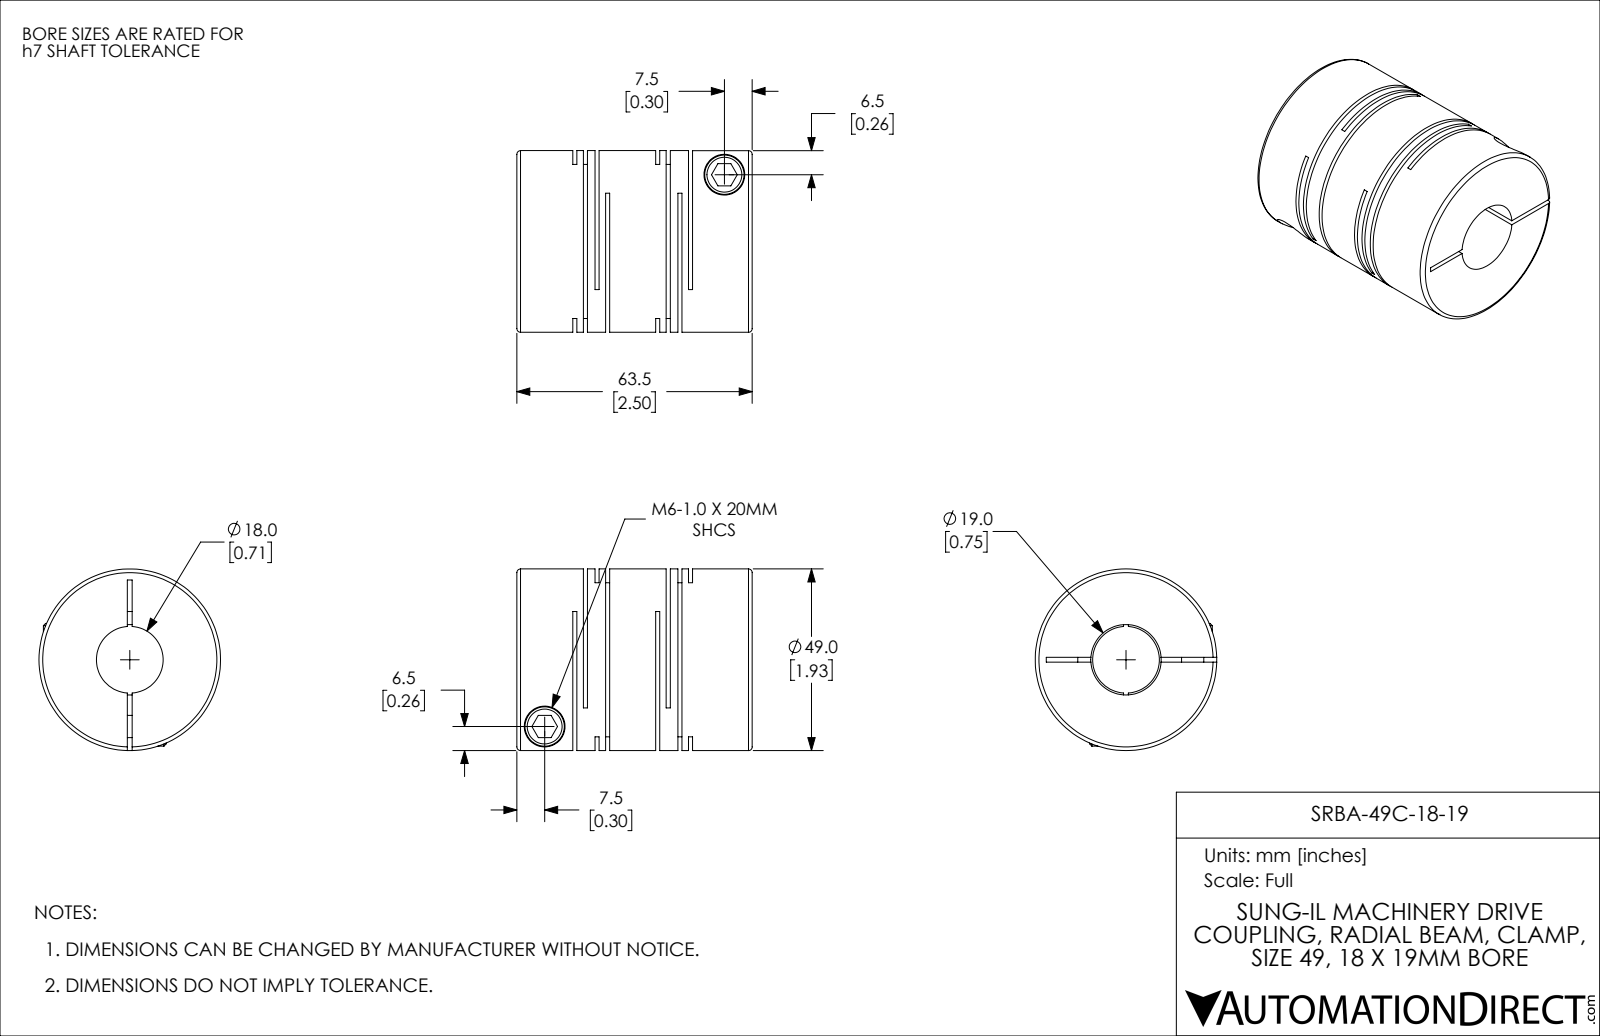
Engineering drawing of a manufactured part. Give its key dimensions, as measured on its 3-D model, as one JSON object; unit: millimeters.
{"part_name": "SRBA-49C-18-19", "step_written_by": "SolidWorks 2021 (CONFIG_CONTROL_DESIGN)", "units": "millimeters", "bodies": {"solids": 1, "faces": 114, "planar": 60, "cylindrical": 42, "other": 12}, "overall_size": [63.5, 49, 49], "volume_mm3": 88284, "surface_area_mm2": 38444, "round_holes": [[6, 2], [11, 2], [18, 1], [19, 1]], "round_bosses_or_shafts": [[10.6, 2], [49, 1]], "face_to_face_distances": [6, 1.1, 22.35, 2.85, 1.75, 4.9, 21.25, 3.15, 19.5, 16.35]}
